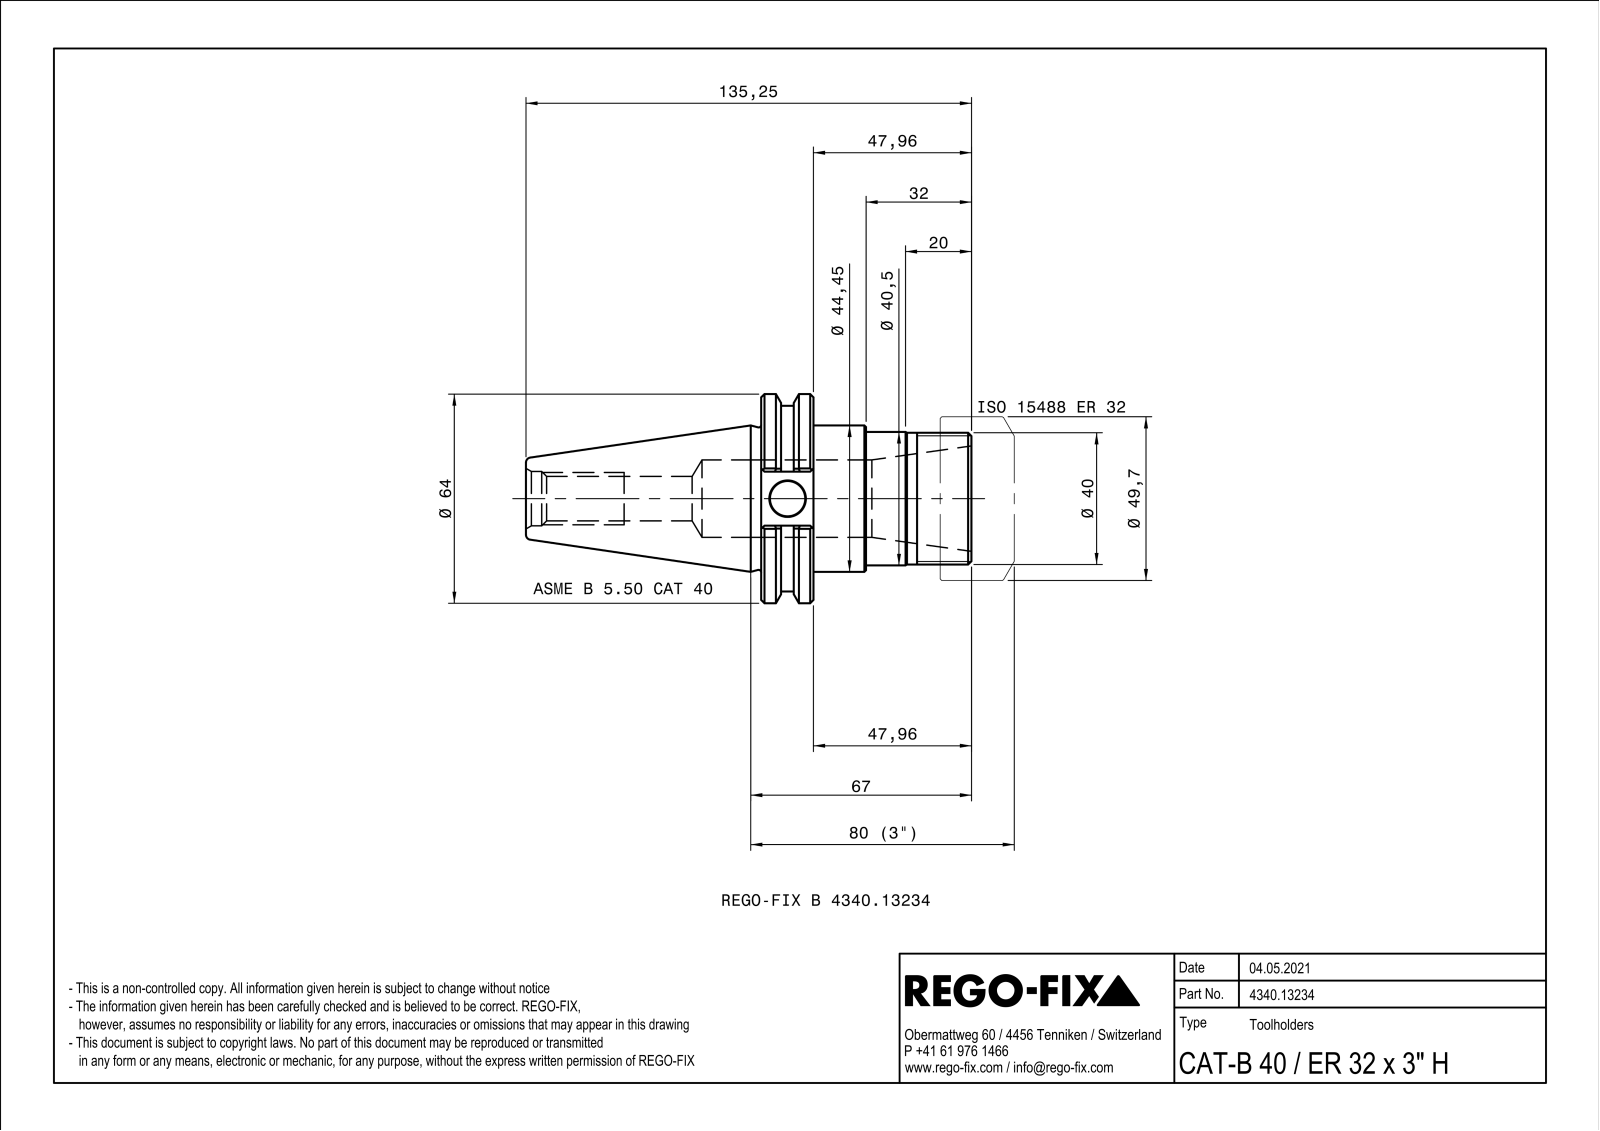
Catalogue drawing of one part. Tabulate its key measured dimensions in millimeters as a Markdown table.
| quantity | value |
| --- | --- |
| part name | NOCUT |
| STEP written by | SIEMENS PLM Software Solid Edge ST10 (AUTOMOTIVE_DESIGN) |
| units | millimeters |
| bodies | 1 solid, 111 faces (31 planar, 32 cylindrical, 48 other) |
| overall size | 135.25 × 63.5 × 60.79 |
| volume | 127 936 mm³ |
| surface area | 31 502 mm² |
| round holes (diameter × count) | 3.24 × 2, 3.9 × 2, 10.7 × 1, 13.5 × 1, 13.53 × 1, 16.5 × 1, 23.5 × 1 |
| round bosses / shafts (diameter × count) | 63.5 × 1, 56.36 × 1, 44.45 × 1, 40.5 × 1, 40 × 1 |
| partial cylindrical surfaces (radius × count) | 0.5 × 4 |
| main face-to-face distances | 15.87, 47.96, 63.83, 47.33, 16.38, 135.25, 87.29, 71.42, 53.95, 5.99 |
